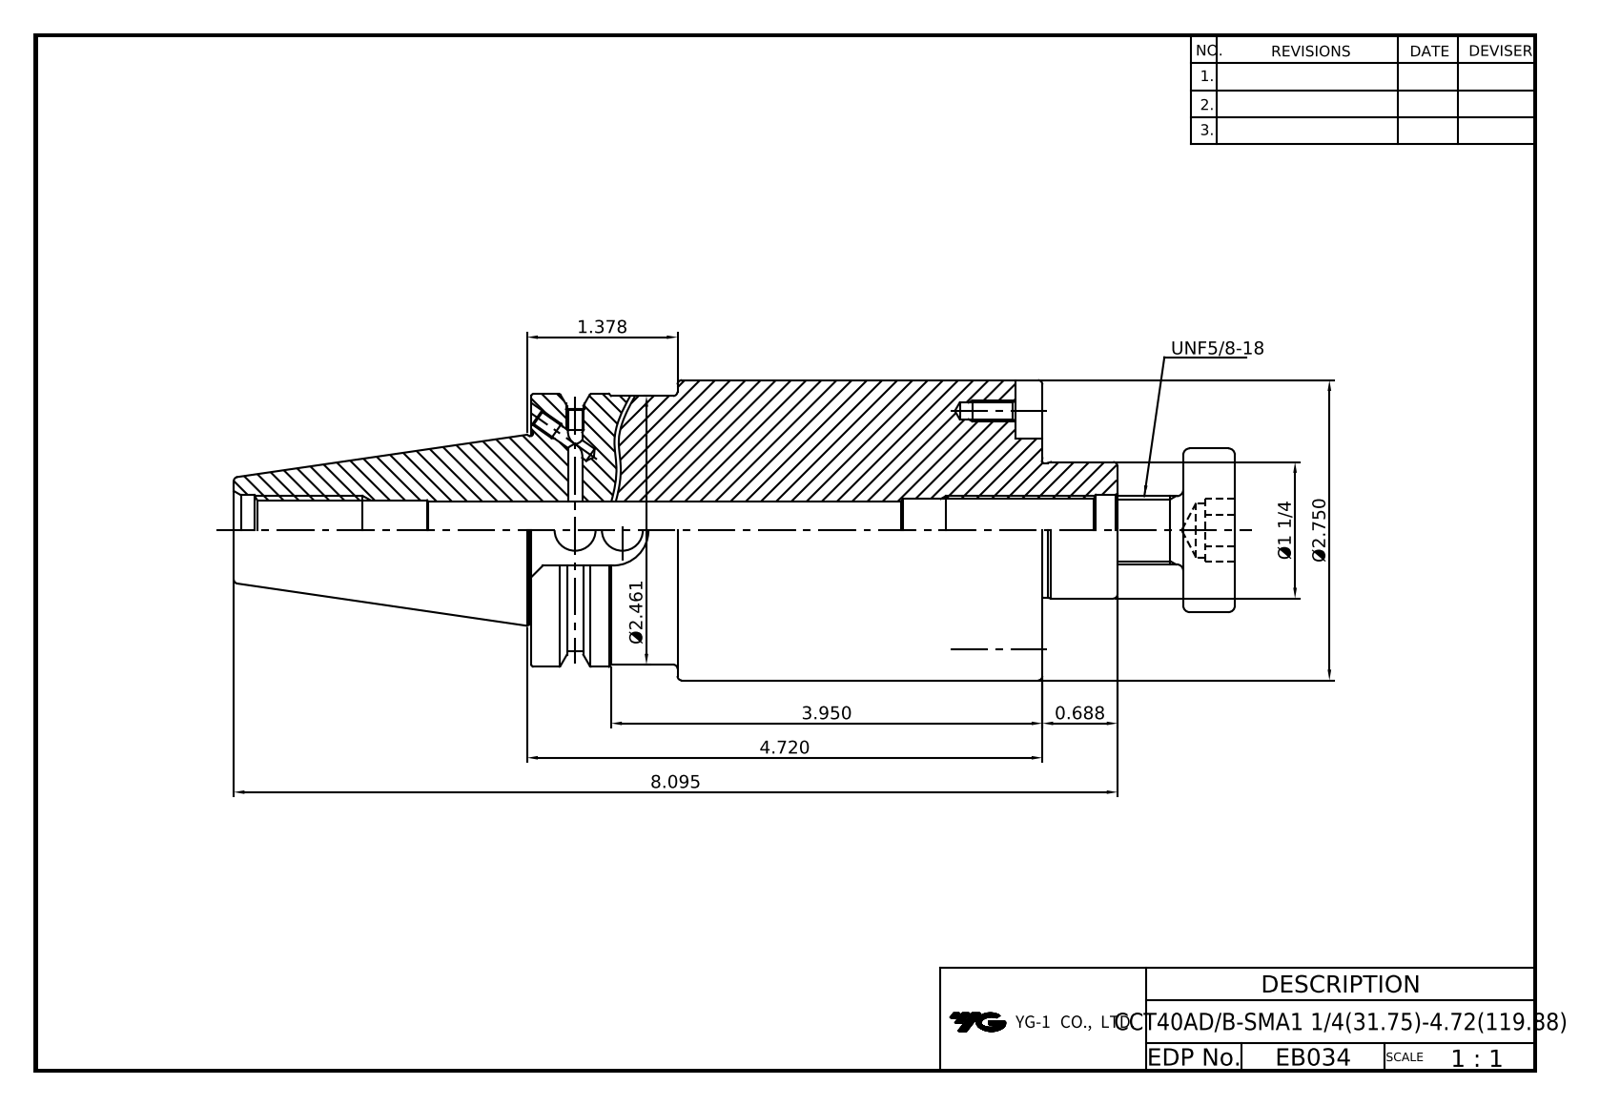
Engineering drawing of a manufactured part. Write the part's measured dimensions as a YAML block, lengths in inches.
part_name: "CCT40ADB-SMA31.75-119.888; DRIVE KEY-12.7x12.7x12.7; HEX'' WRENCH BOLT-UNC#10-24x1_2L; COLLAR BOLT-UNF5_8-18x40L"
step_written_by: "Autodesk Inventor 2022 (AUTOMOTIVE_DESIGN)"
units: inches
bodies: {solids: 6, faces: 185, planar: 90, cylindrical: 50, other: 45}
overall_size: [8.961, 2.75, 2.75]
volume: 30.12
surface_area: 94.53
round_holes:
  - {diameter: 0.128, count: 4}
  - {diameter: 0.145, count: 2}
  - {diameter: 0.157, count: 2}
  - {diameter: 0.165, count: 2}
  - {diameter: 0.217, count: 2}
  - {diameter: 0.343, count: 2}
  - {diameter: 0.375, count: 1}
  - {diameter: 0.5, count: 1}
  - {diameter: 0.512, count: 1}
  - {diameter: 0.527, count: 1}
  - {diameter: 0.565, count: 1}
  - {diameter: 0.642, count: 1}
round_bosses_or_shafts:
  - {diameter: 0.312, count: 2}
  - {diameter: 0.19, count: 2}
  - {diameter: 2.75, count: 1}
  - {diameter: 2.5, count: 1}
  - {diameter: 2.461, count: 1}
  - {diameter: 1.724, count: 1}
  - {diameter: 1.5, count: 1}
  - {diameter: 1.25, count: 1}
partial_cylinders:
  - {radius: 0.25, count: 2}
  - {radius: 0.322, count: 1}
  - {radius: 1.108, count: 1}
face_to_face_distances: [4.681, 6.235, 1.554, 5.763, 1.082, 0.472, 0.25, 0.5, 4.431, 1.332]
hole_center_spacings: [1.093, 1.094, 2.187, 2.187, 2.187]
